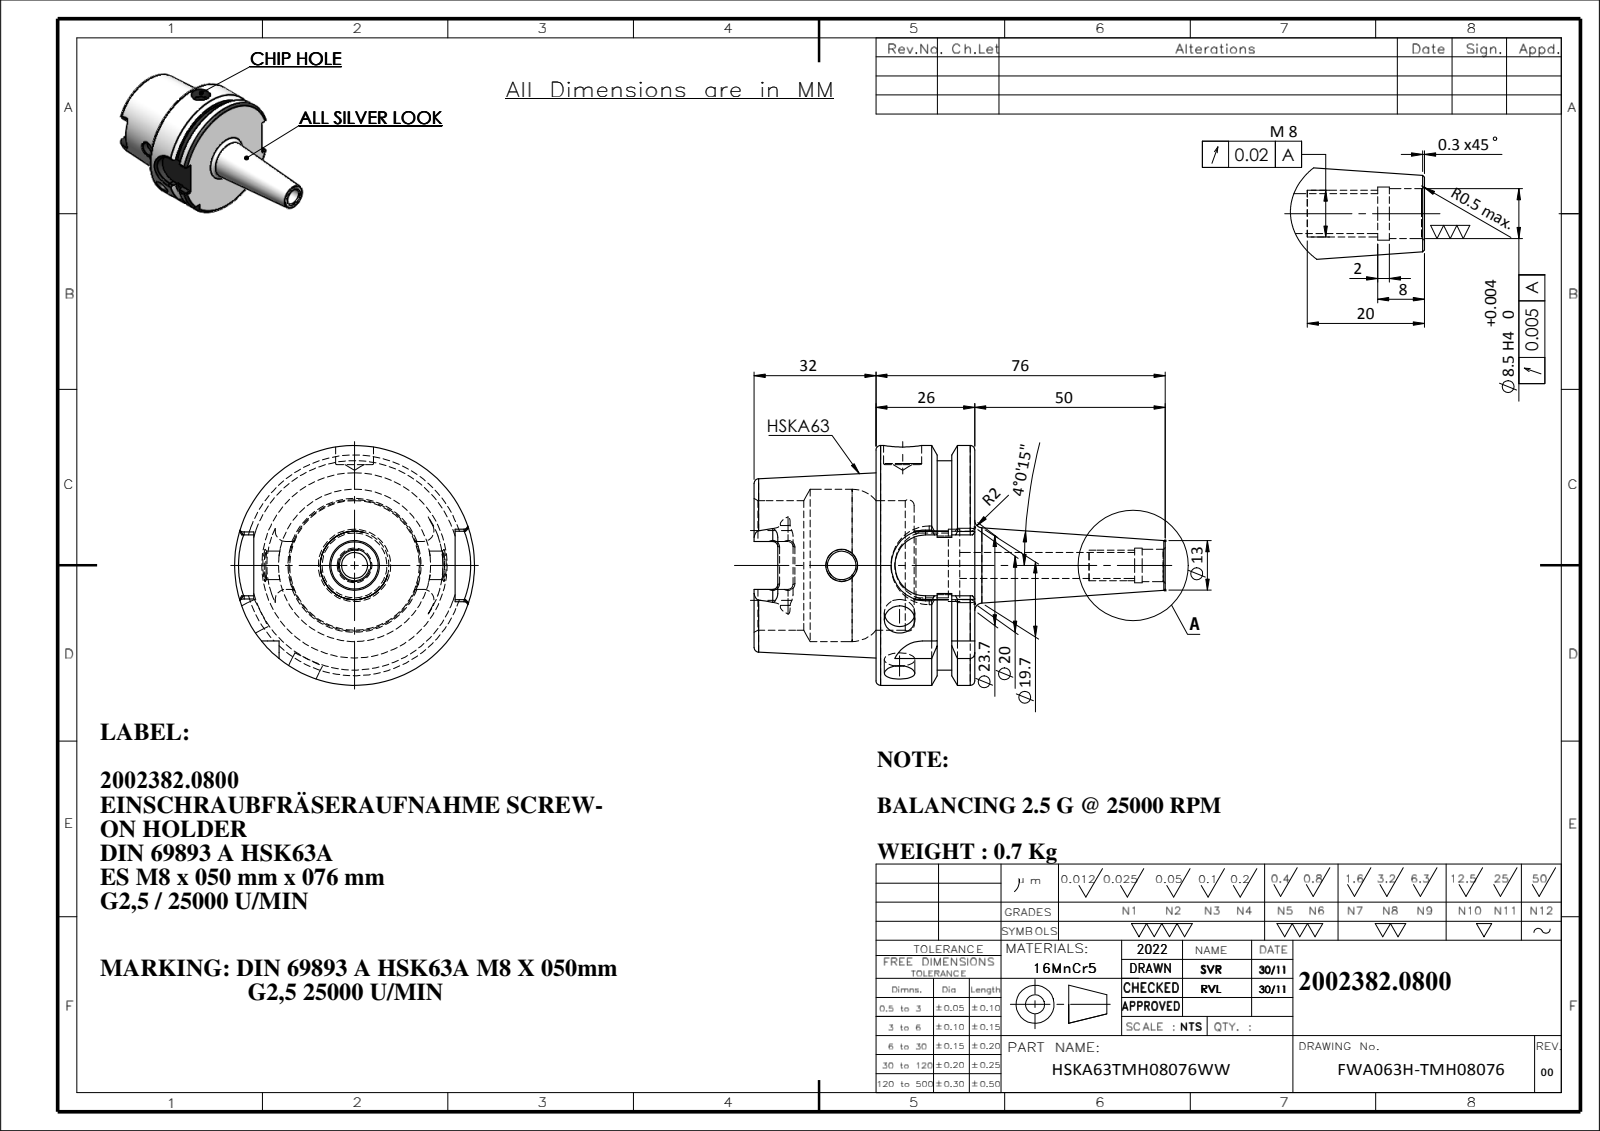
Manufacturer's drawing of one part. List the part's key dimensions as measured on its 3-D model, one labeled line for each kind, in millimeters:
Part name (STEP PRODUCT): 9163A-ES8M08050
STEP written by: SolidWorks 2018 (CONFIG_CONTROL_DESIGN)
Units: millimetres
Bodies: 1 solid, 164 faces (51 planar, 49 cylindrical, 64 other)
Overall size (bounding box): 107.95 × 63 × 63
Volume: 89 786 mm³ · Surface area: 25 848 mm²
Round holes (diameter × count): ⌀8 ×2, ⌀6.8 ×1, ⌀7.5 ×1, ⌀8.5 ×1, ⌀9.1 ×1, ⌀10 ×1, ⌀17 ×1, ⌀19 ×1, ⌀34 ×1, ⌀40 ×1
Round bosses / shafts (diameter × count): ⌀63 ×1, ⌀55 ×1
Partial cylindrical surfaces — rounded edges, fillets, slot ends (radius × count): R1.3 ×6, R2.88 ×4, R8 ×2, R9 ×1
Main face-to-face distances: 25.95, 10, 15.95, 42, 57.95, 32, 52.9, 54, 22, 12
